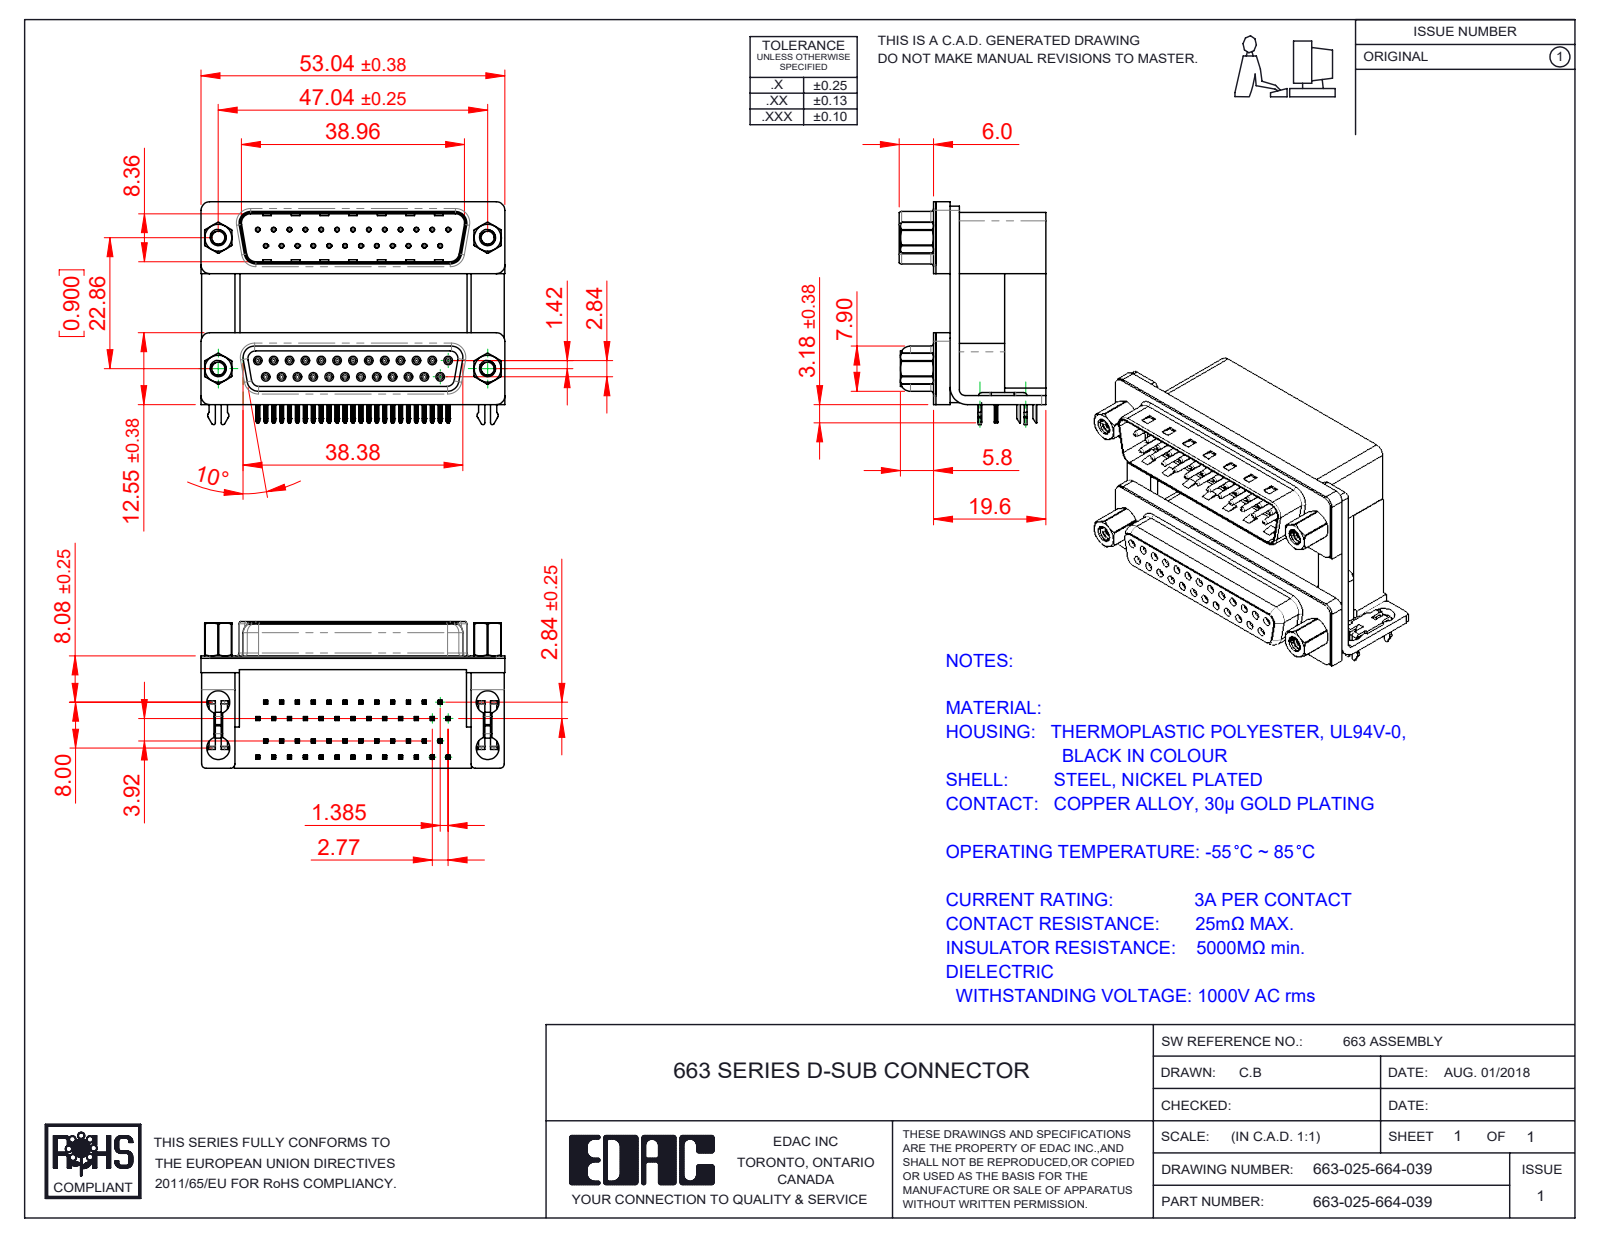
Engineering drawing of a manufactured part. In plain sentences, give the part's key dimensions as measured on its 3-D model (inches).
The part is named "663 Housing Upper_25 Contacts H; 663 Contact Bottom Upper_H; 663 4-40 Hex Standoff 5; 663 Mounting Bracket_2ProngH (+8 more)". Its 3-D file was written by "SolidWorks 2020 (CONFIG_CONTROL_DESIGN)". It is 67 solids with 6607 faces: 3403 planar, 1737 cylindrical and 1467 other. Overall it measures 2.088 by 1.532 by 1.008 inches. Its volume is 1.474 cubic inches and its surface area 40.53 square inches. Round holes: 50 of diameter 0.031, 25 of diameter 0.014, 25 of diameter 0.035, 8 of diameter 0.157, 4 of diameter 0.089, 4 of diameter 0.09, 4 of diameter 0.138, 4 of diameter 0.189, 4 of diameter 0.197. Round bosses or shafts: 25 of diameter 0.047, 25 of diameter 0.03, 4 of diameter 0.193, 4 of diameter 0.187, 4 of diameter 0.154, 4 of diameter 0.11. Partial cylindrical surfaces (rounded edges, fillets, slot ends): 202 of radius 0.004, 110 of radius 0.01, 100 of radius 0.006, 50 of radius 0.005, 50 of radius 0.014, 25 of radius 0.013, 16 of radius 0.02, 14 of radius 0.059. The main face-to-face distances are 0.756, 0.472, 0.016, 0.283, 0.421, 0.657, 0.374, 0.098, 0.488, 0.9. The hole center spacings are 0.124, 0.109, 0.218, 0.436, 0.327, 0.198, 0.545, 0.294.
